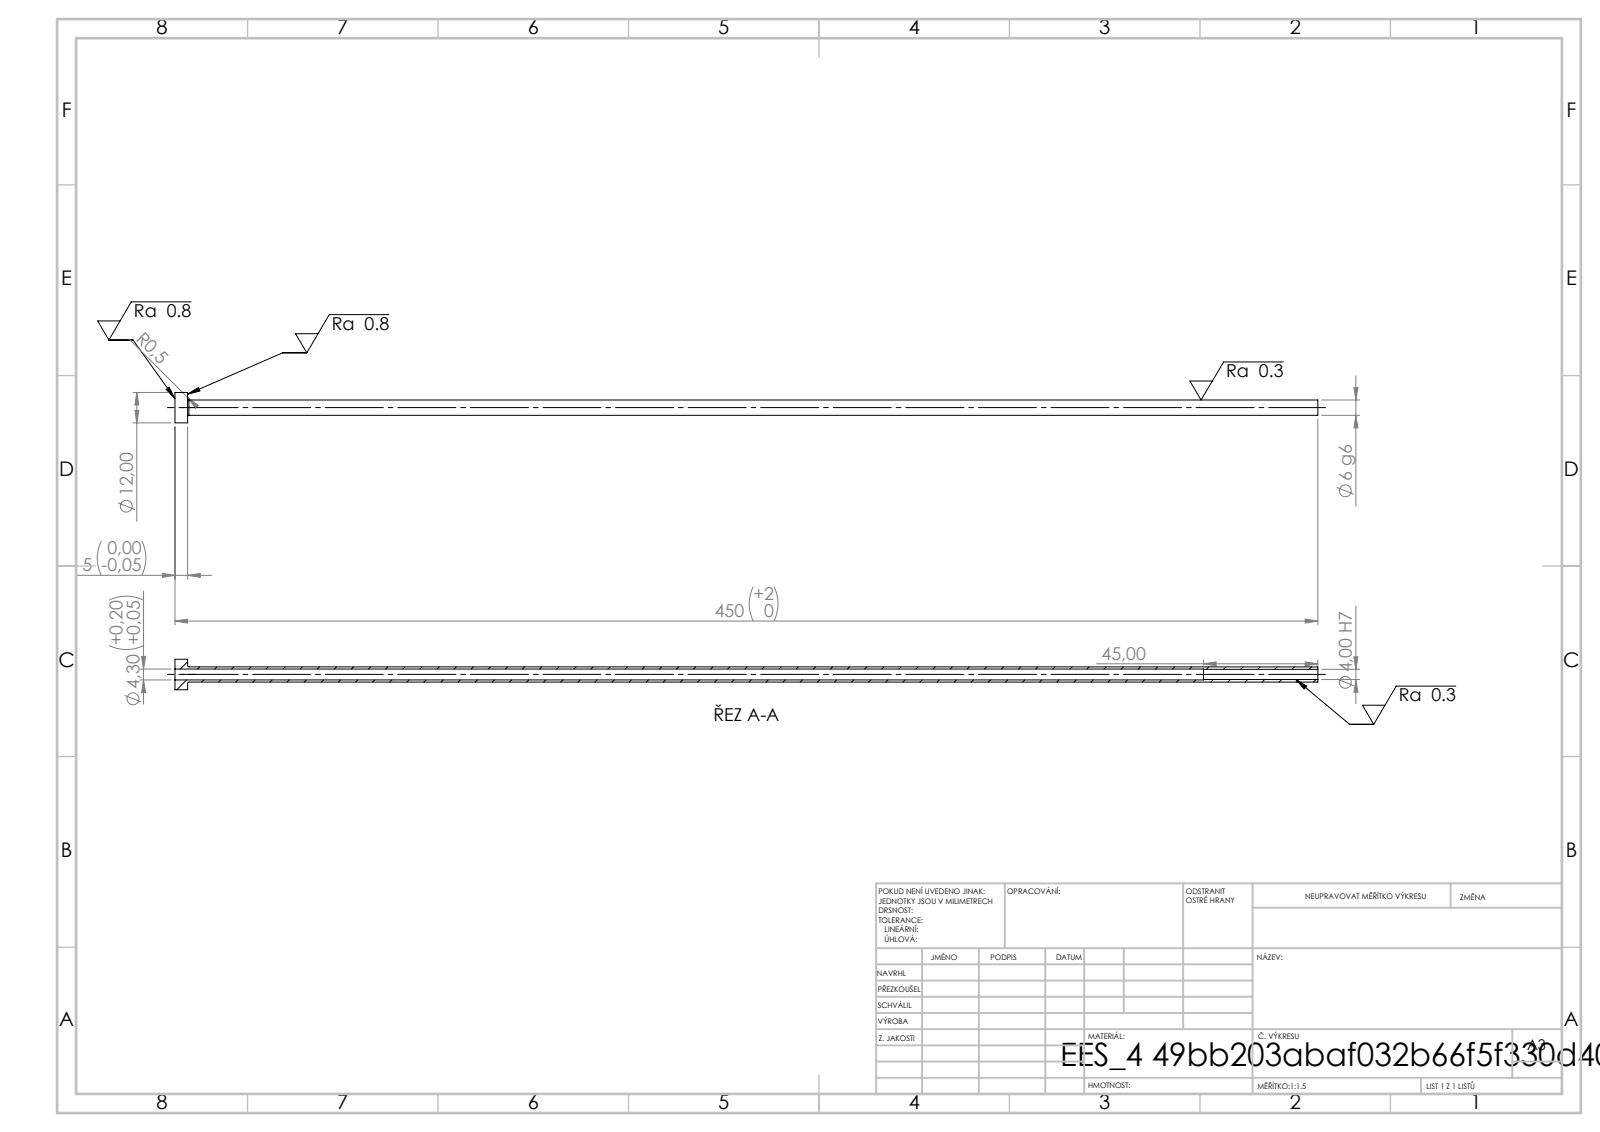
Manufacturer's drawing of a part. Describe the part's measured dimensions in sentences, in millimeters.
Its 3-D file was written by "SolidWorks 2019 (CONFIG_CONTROL_DESIGN)". It is 1 solid with 14 faces: 4 planar, 8 cylindrical and 2 other. Overall it measures 450 by 12 by 12 millimeters. Its volume is 6 702 cubic millimeters and its surface area 14 810 square millimeters. Round holes: 1 of diameter 4, 1 of diameter 4.3. Round bosses or shafts: 1 of diameter 12, 1 of diameter 6. The main face-to-face distances are 5, 450, 445, 405, 400, 45.
